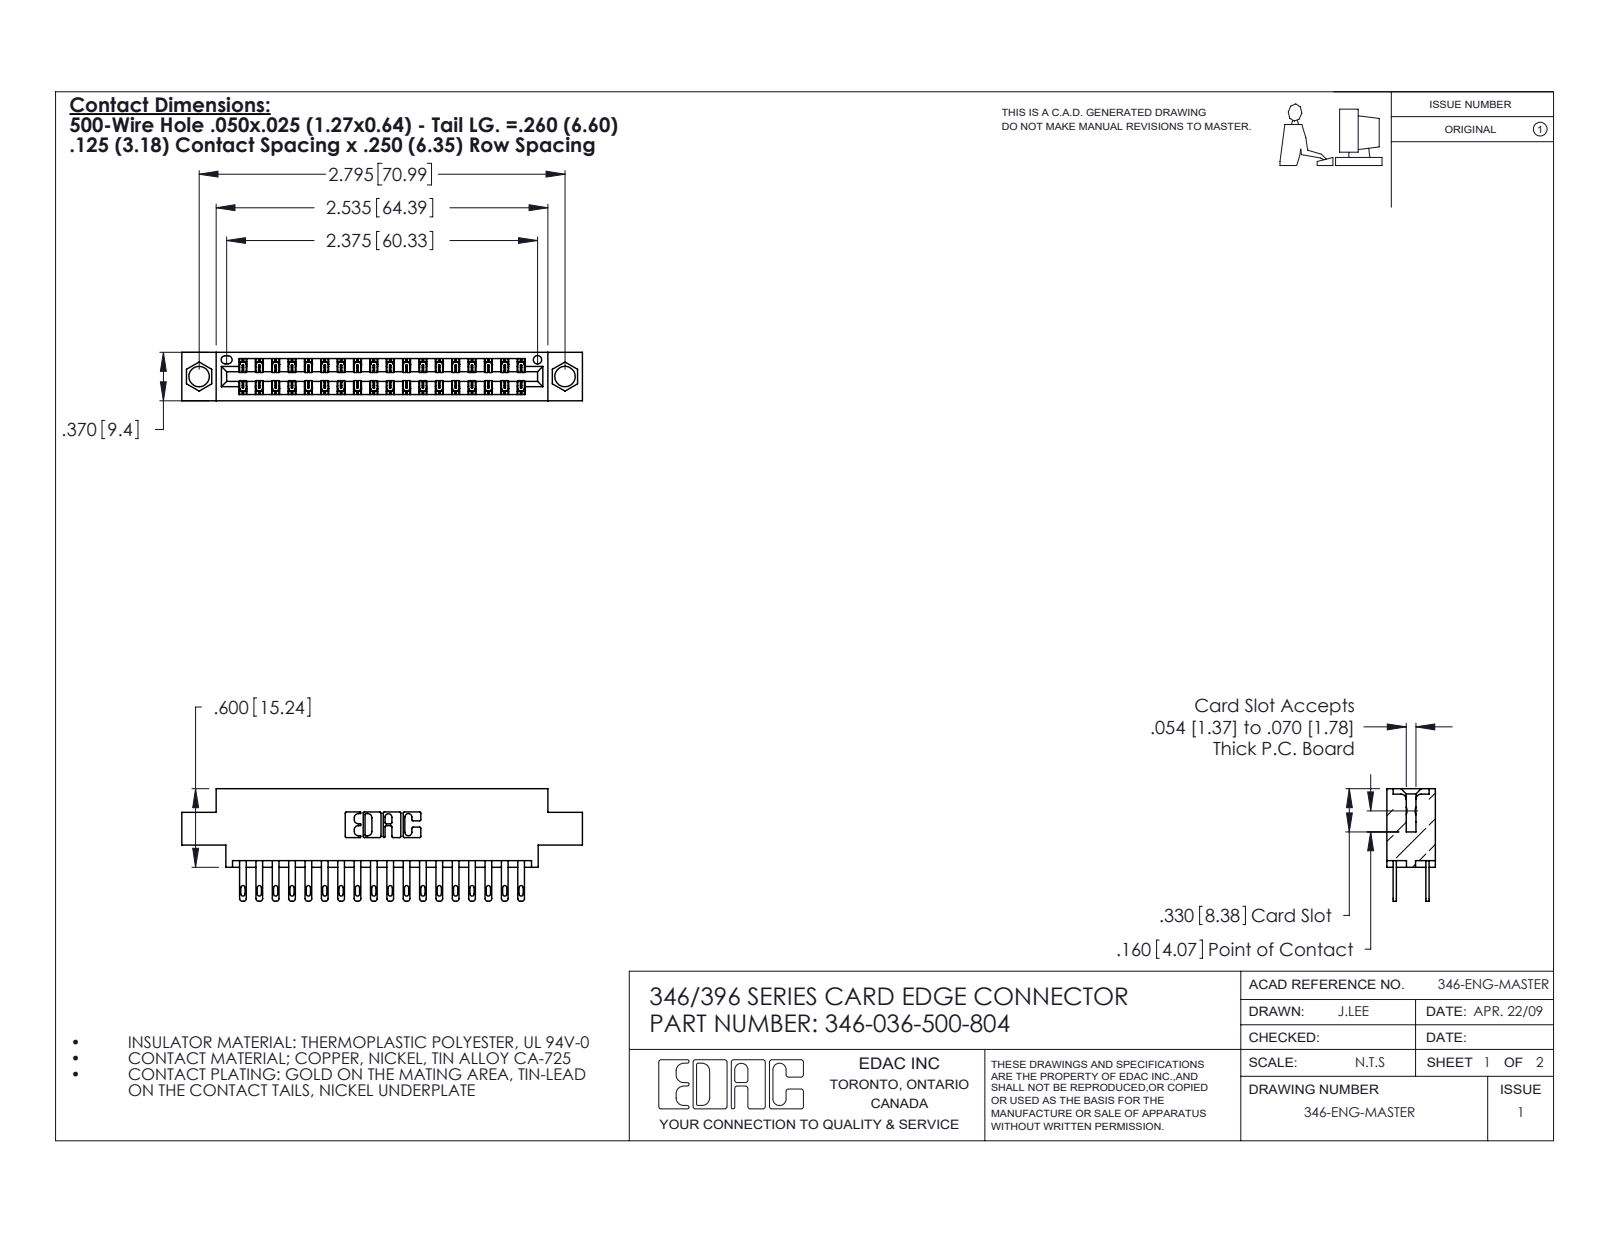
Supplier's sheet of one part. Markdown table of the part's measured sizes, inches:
| quantity | value |
| --- | --- |
| part name | 345-292-001_345-293-100; 346 Part_0.170 Offset - 0.156 Dia-TH; 346-036-500-804 |
| STEP written by | SolidWorks 2020 (CONFIG_CONTROL_DESIGN) |
| units | inches |
| bodies | 37 solids, 1868 faces (1138 planar, 730 cylindrical, 0 other) |
| overall size | 3.06 × 0.86 × 0.37 |
| volume | 0.442 in³ |
| surface area | 15.47 in² |
| round holes (diameter × count) | 0.156 × 2, 0.064 × 1 |
| partial cylindrical surfaces (radius × count) | 0.006 × 54, 0.016 × 36, 0.02 × 36, 0.01 × 22, 0.007 × 6, 0.031 × 6, 0.026 × 3, 0.014 × 2 |
| main face-to-face distances | 0.048, 0.322, 0.25, 0.37, 0.072, 0.298, 0.025, 0.275, 0.222, 0.148 |
| hole center spacings | 0.246, 2.588, 2.795 |
